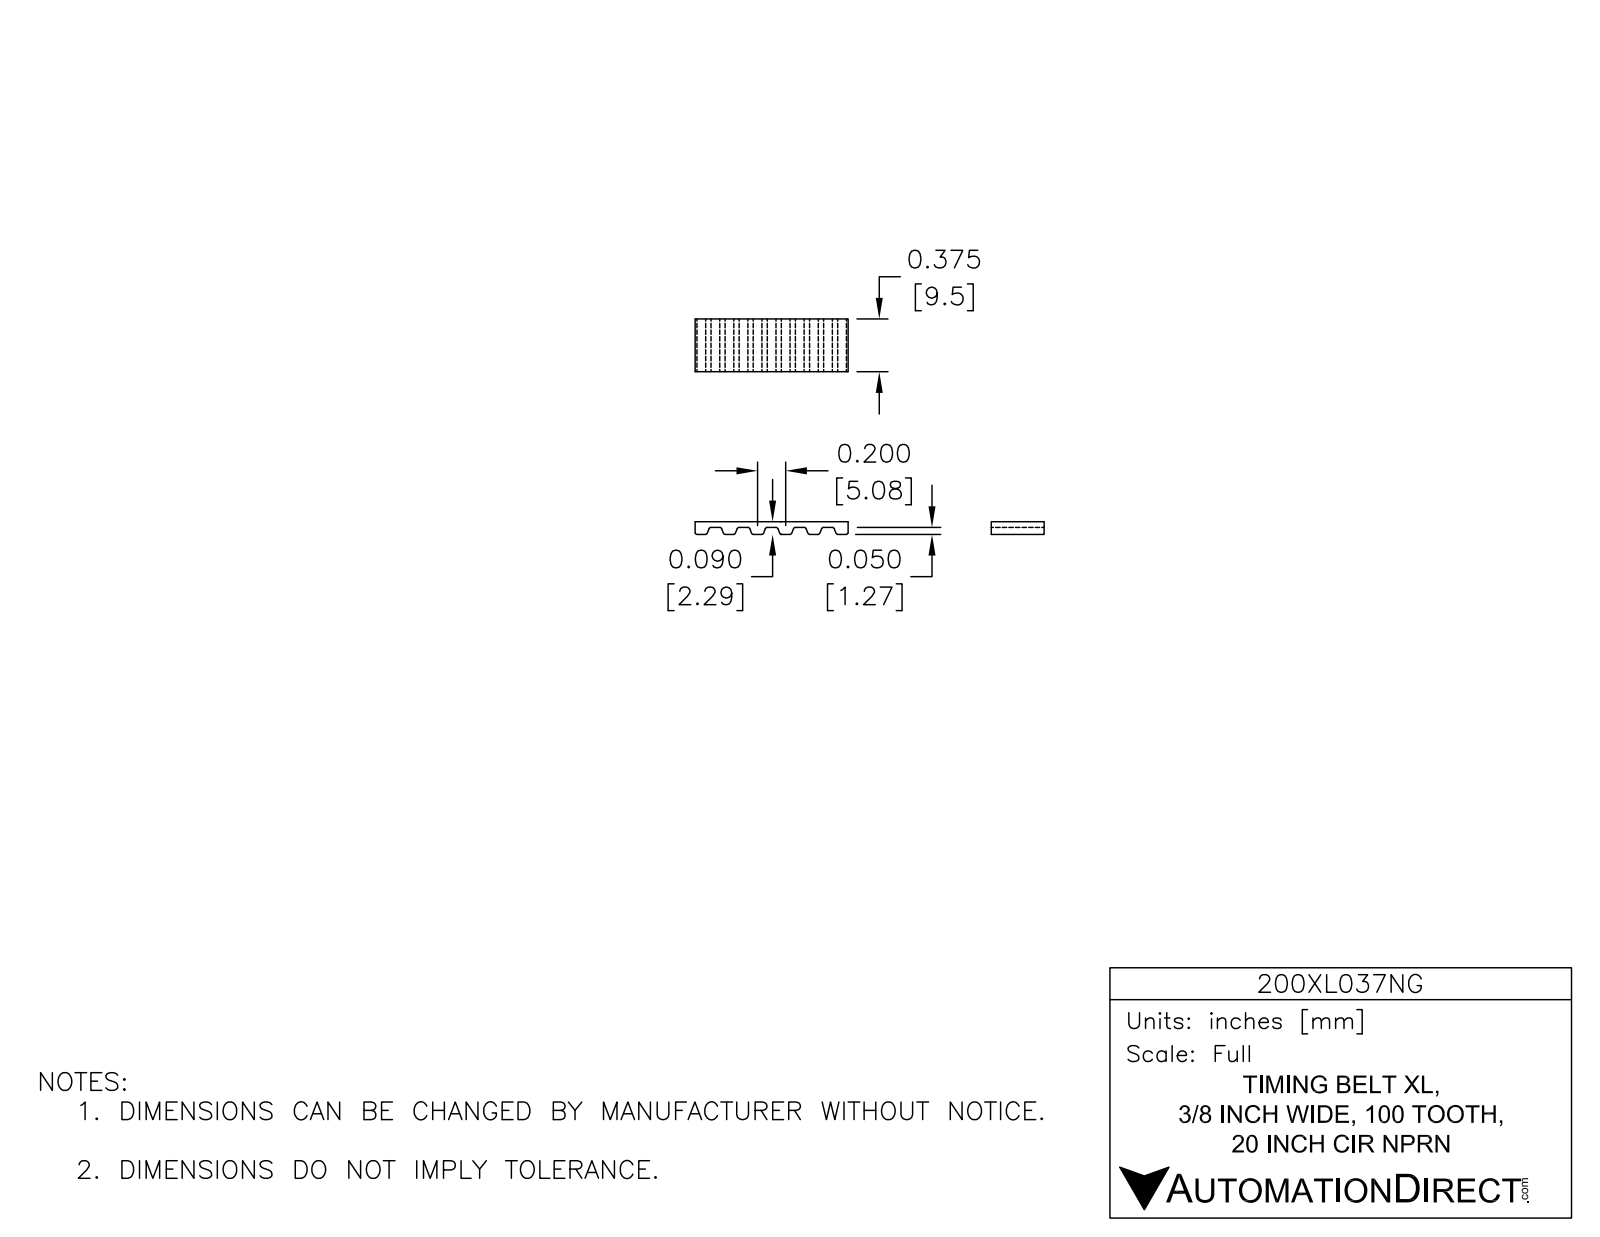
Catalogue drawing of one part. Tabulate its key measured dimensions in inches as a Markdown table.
| quantity | value |
| --- | --- |
| part name | 200XL037NG |
| STEP written by | SolidWorks 2014 (AUTOMOTIVE_DESIGN) |
| units | inches |
| bodies | 1 solid, 840 faces (360 planar, 480 cylindrical, 0 other) |
| overall size | 8.288 × 3 × 0.375 |
| volume | 0.408 in³ |
| surface area | 19.15 in² |
| partial cylindrical surfaces (radius × count) | 0.015 × 400, 1.46 × 2, 1.5 × 2 |
| main face-to-face distances | 3, 0.04, 2.96, 0.375, 2.92, 0.358, 0.09, 2.91, 0.05, 2.87 |
